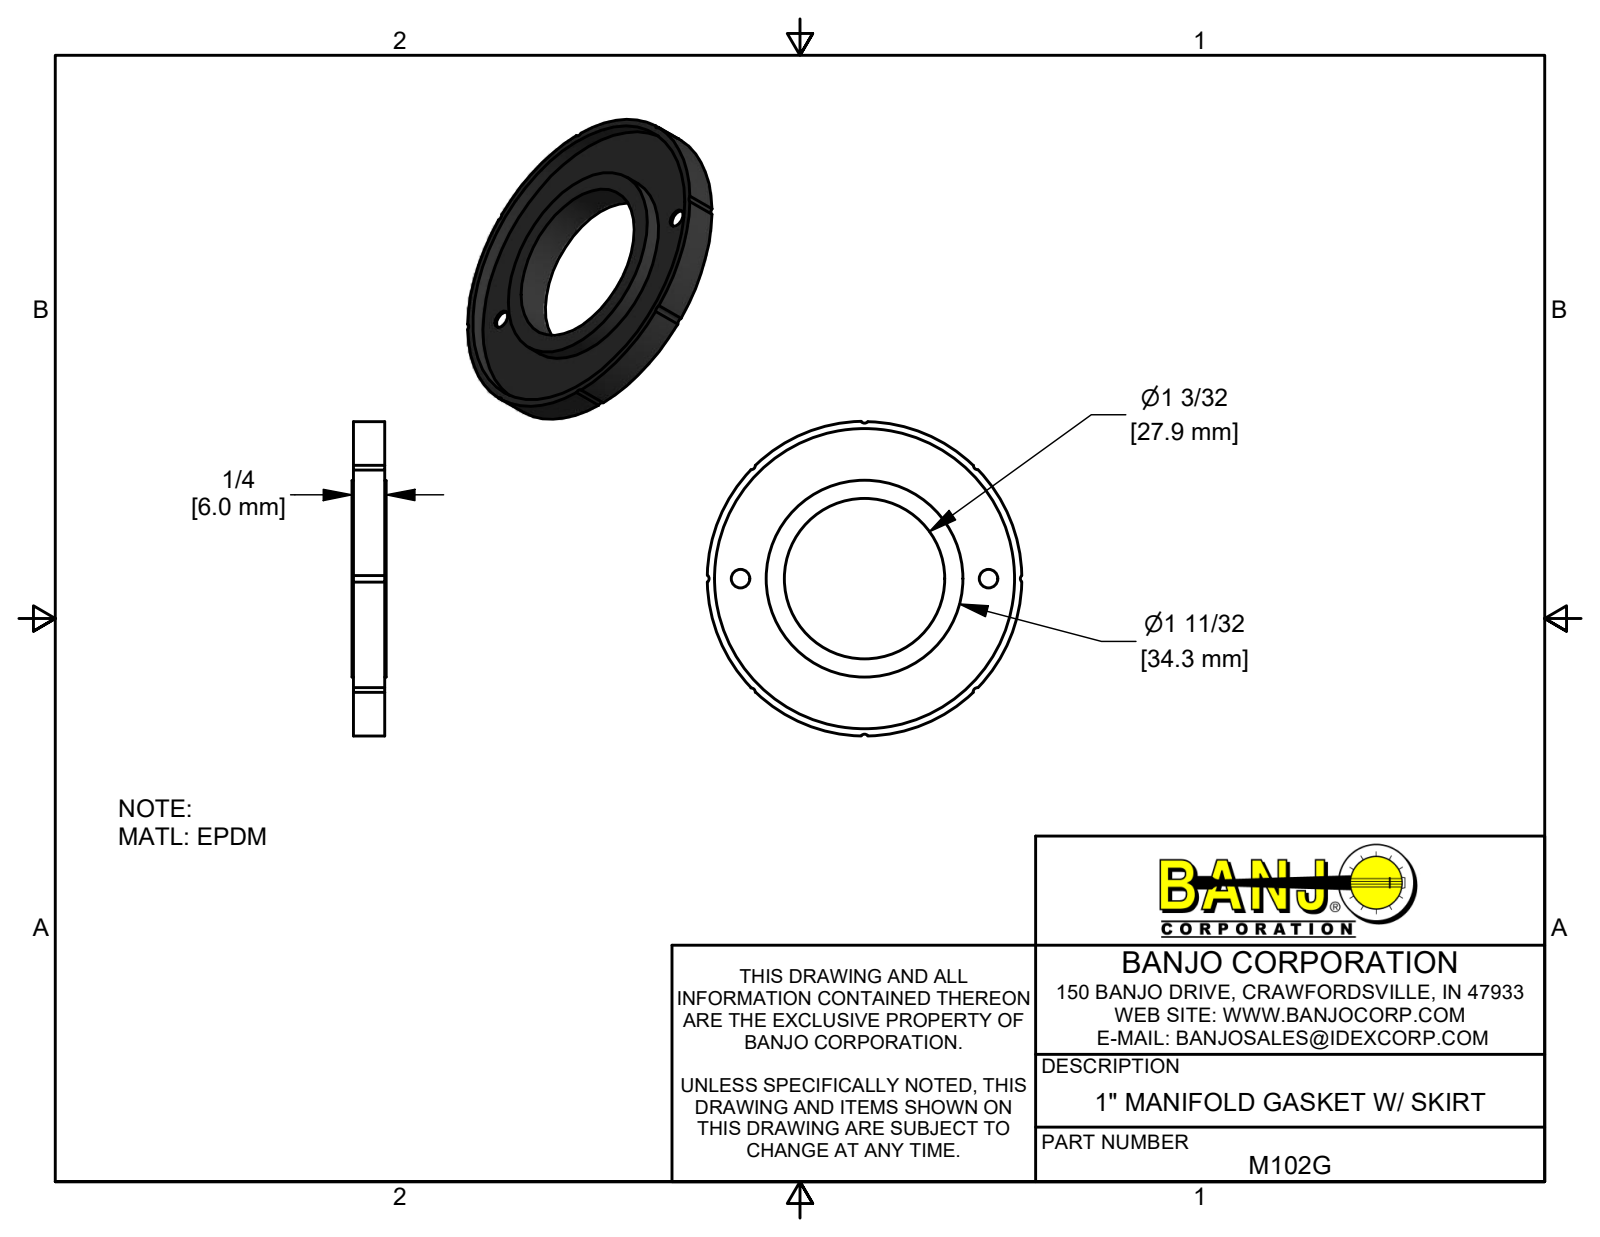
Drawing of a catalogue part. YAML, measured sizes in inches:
part_name: "M102G"
step_written_by: "Autodesk Inventor 2019 (AUTOMOTIVE_DESIGN)"
units: inches
bodies: {solids: 1, faces: 29, planar: 6, cylindrical: 23, other: 0}
overall_size: [2.16, 2.16, 0.235]
volume: 0.214
surface_area: 9.884
round_holes:
  - {diameter: 0.125, count: 2}
  - {diameter: 1.1, count: 1}
  - {diameter: 2.06, count: 1}
round_bosses_or_shafts:
  - {diameter: 2.16, count: 1}
  - {diameter: 1.35, count: 1}
partial_cylinders:
  - {radius: 0.03, count: 8}
face_to_face_distances: [0.016, 0.109, 0.126, 0.235, 0.1, 0.116, 0.225, 0.225, 0.215, 0.115]
hole_center_spacings: [0.852, 1.705]
